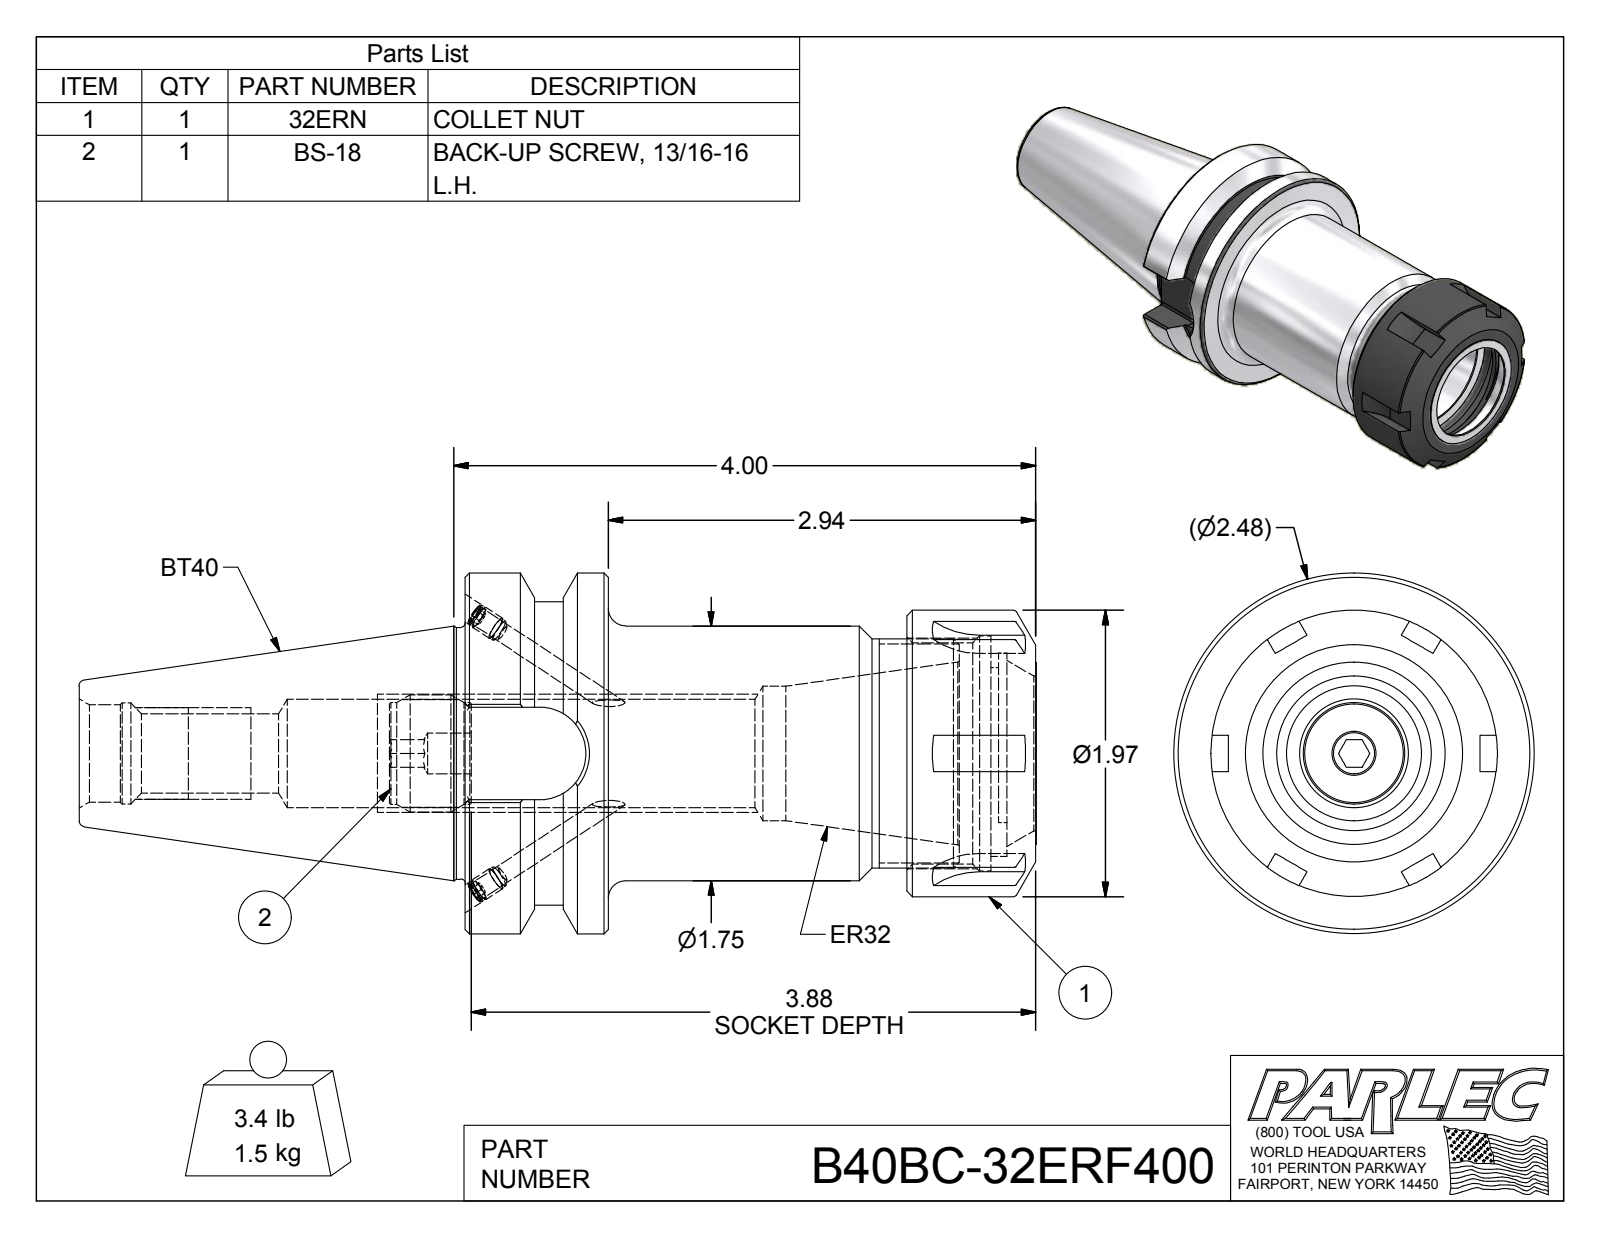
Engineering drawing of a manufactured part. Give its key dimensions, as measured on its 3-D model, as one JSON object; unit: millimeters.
{"part_name": "B40BCB-32ER4-1; 029-965; 32ERN; BS-18 (+1 more)", "step_written_by": "Autodesk Inventor 2016 (AUTOMOTIVE_DESIGN)", "units": "millimeters", "bodies": {"solids": 5, "faces": 211, "planar": 88, "cylindrical": 56, "other": 67}, "overall_size": [167, 62.99, 62.99], "volume_mm3": 196026, "surface_area_mm2": 46569, "round_holes": [[3.3, 2], [4.1, 2], [7.11, 1], [13.84, 1], [17.01, 1], [17.62, 1], [18.92, 1], [23.5, 1], [27, 1], [33.02, 1], [38.65, 1], [41, 1]], "round_bosses_or_shafts": [[4.2, 2], [4, 2], [62.99, 1], [53.01, 1], [50, 1], [44.45, 1], [43.94, 1], [40, 1]], "partial_cylinders_radius": [[0.51, 20], [8.09, 1], [14.9, 1], [17.5, 1]], "face_to_face_distances": [24.99, 99.62, 74.63, 76.84, 51.85, 22.78, 91.85, 66.86, 15.01, 7.77], "hole_center_spacings": [1.85]}
